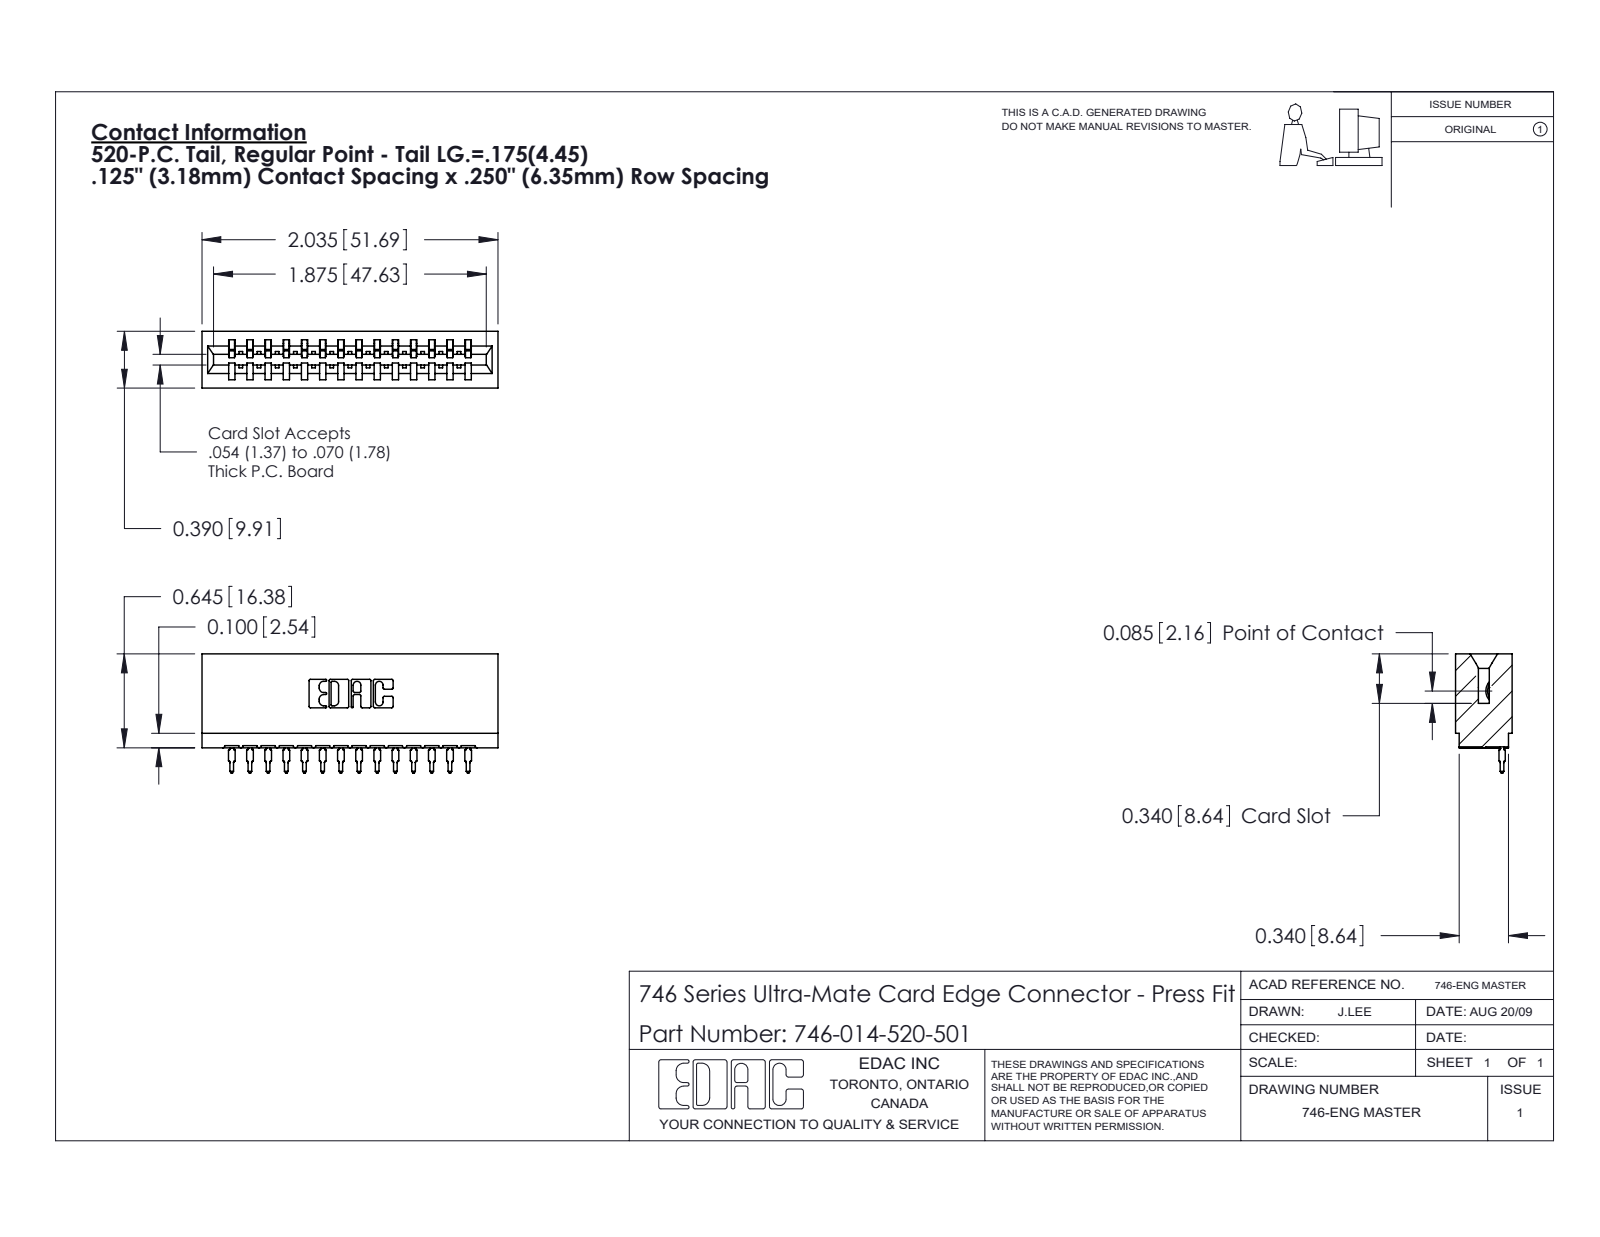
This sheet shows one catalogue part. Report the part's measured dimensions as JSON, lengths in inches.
{"part_name": "746 Part_.340 Slot Depth - 01; 746-014-520-501; 746-292-001_520", "step_written_by": "SolidWorks 2020 (CONFIG_CONTROL_DESIGN)", "units": "inches", "bodies": {"solids": 15, "faces": 1609, "planar": 937, "cylindrical": 308, "other": 364}, "overall_size": [2.035, 0.819, 0.39], "volume_in3": 0.363, "surface_area_in2": 11.62, "partial_cylinders_radius": [[0.021, 28], [0.01, 22], [0.015, 15], [0.007, 6], [0.031, 6], [0.005, 4], [0.011, 4], [0.026, 3]], "face_to_face_distances": [0.25, 0.333, 0.5, 0.057, 0.39, 0.125, 0.292, 0.125, 0.042, 0.542]}
